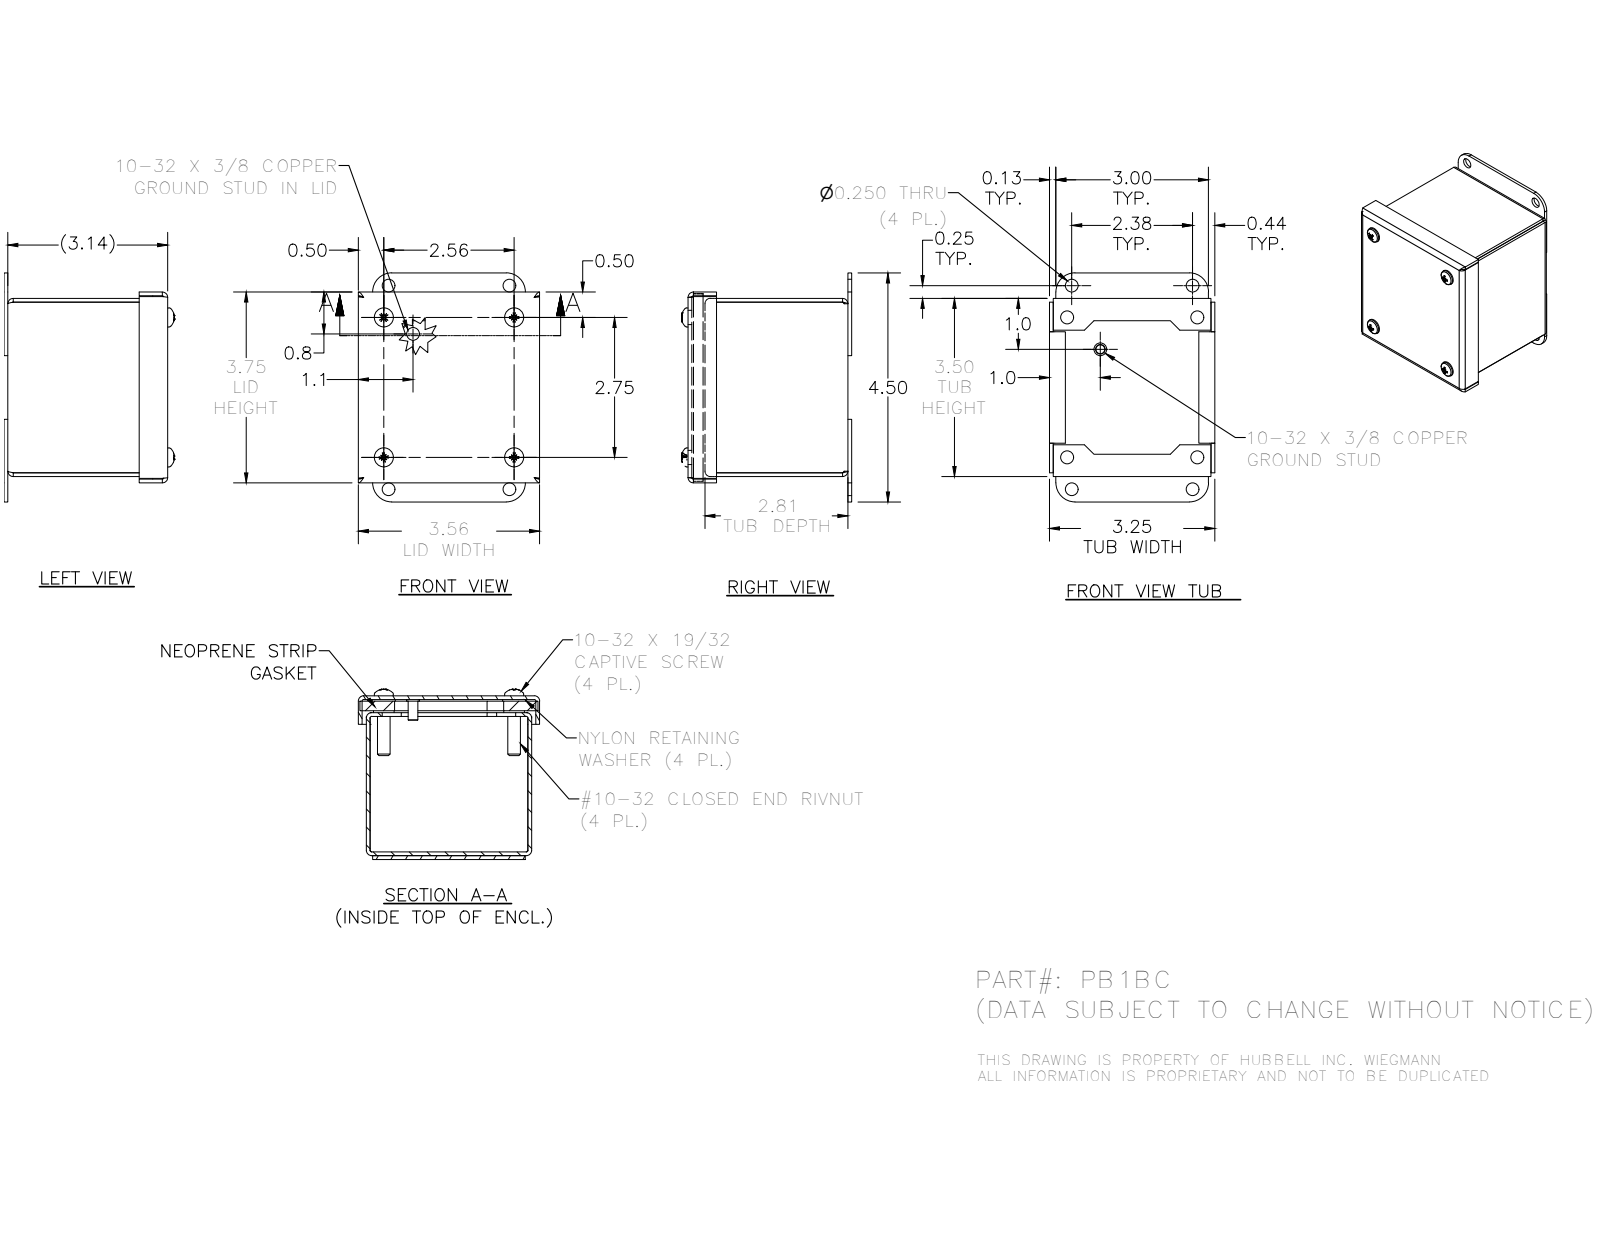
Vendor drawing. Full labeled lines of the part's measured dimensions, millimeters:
Part name (STEP PRODUCT): 39077; 316256; 372163; PB1BCBKP (+5 more)
STEP written by: Autodesk Inventor 2016 (AUTOMOTIVE_DESIGN)
Units: millimetres
Bodies: 19 solids, 478 faces (268 planar, 96 cylindrical, 114 other)
Overall size (bounding box): 114.3 × 90.49 × 84.99
Volume: 119 119 mm³ · Surface area: 123 226 mm²
Round holes (diameter × count): ⌀3.96 ×4, ⌀4.98 ×4, ⌀6.35 ×4, ⌀6.53 ×4, ⌀7.06 ×4, ⌀7.14 ×4, ⌀7.95 ×4
Round bosses / shafts (diameter × count): ⌀4.83 ×6, ⌀11.51 ×4, ⌀10.31 ×4, ⌀9.47 ×4, ⌀6.3 ×4, ⌀6.35 ×2
Partial cylindrical surfaces — rounded edges, fillets, slot ends (radius × count): R0.79 ×12, R2.67 ×12, R2.27 ×4, R9.53 ×4
Main face-to-face distances: 1.88, 77.93, 79.81, 80.67, 76.05, 3.76, 81.69, 82.55, 78.79, 1.87
Hole centre spacings: 69.85, 16.05, 85.75, 85.76, 95.46, 65.05, 95.45, 106.21
